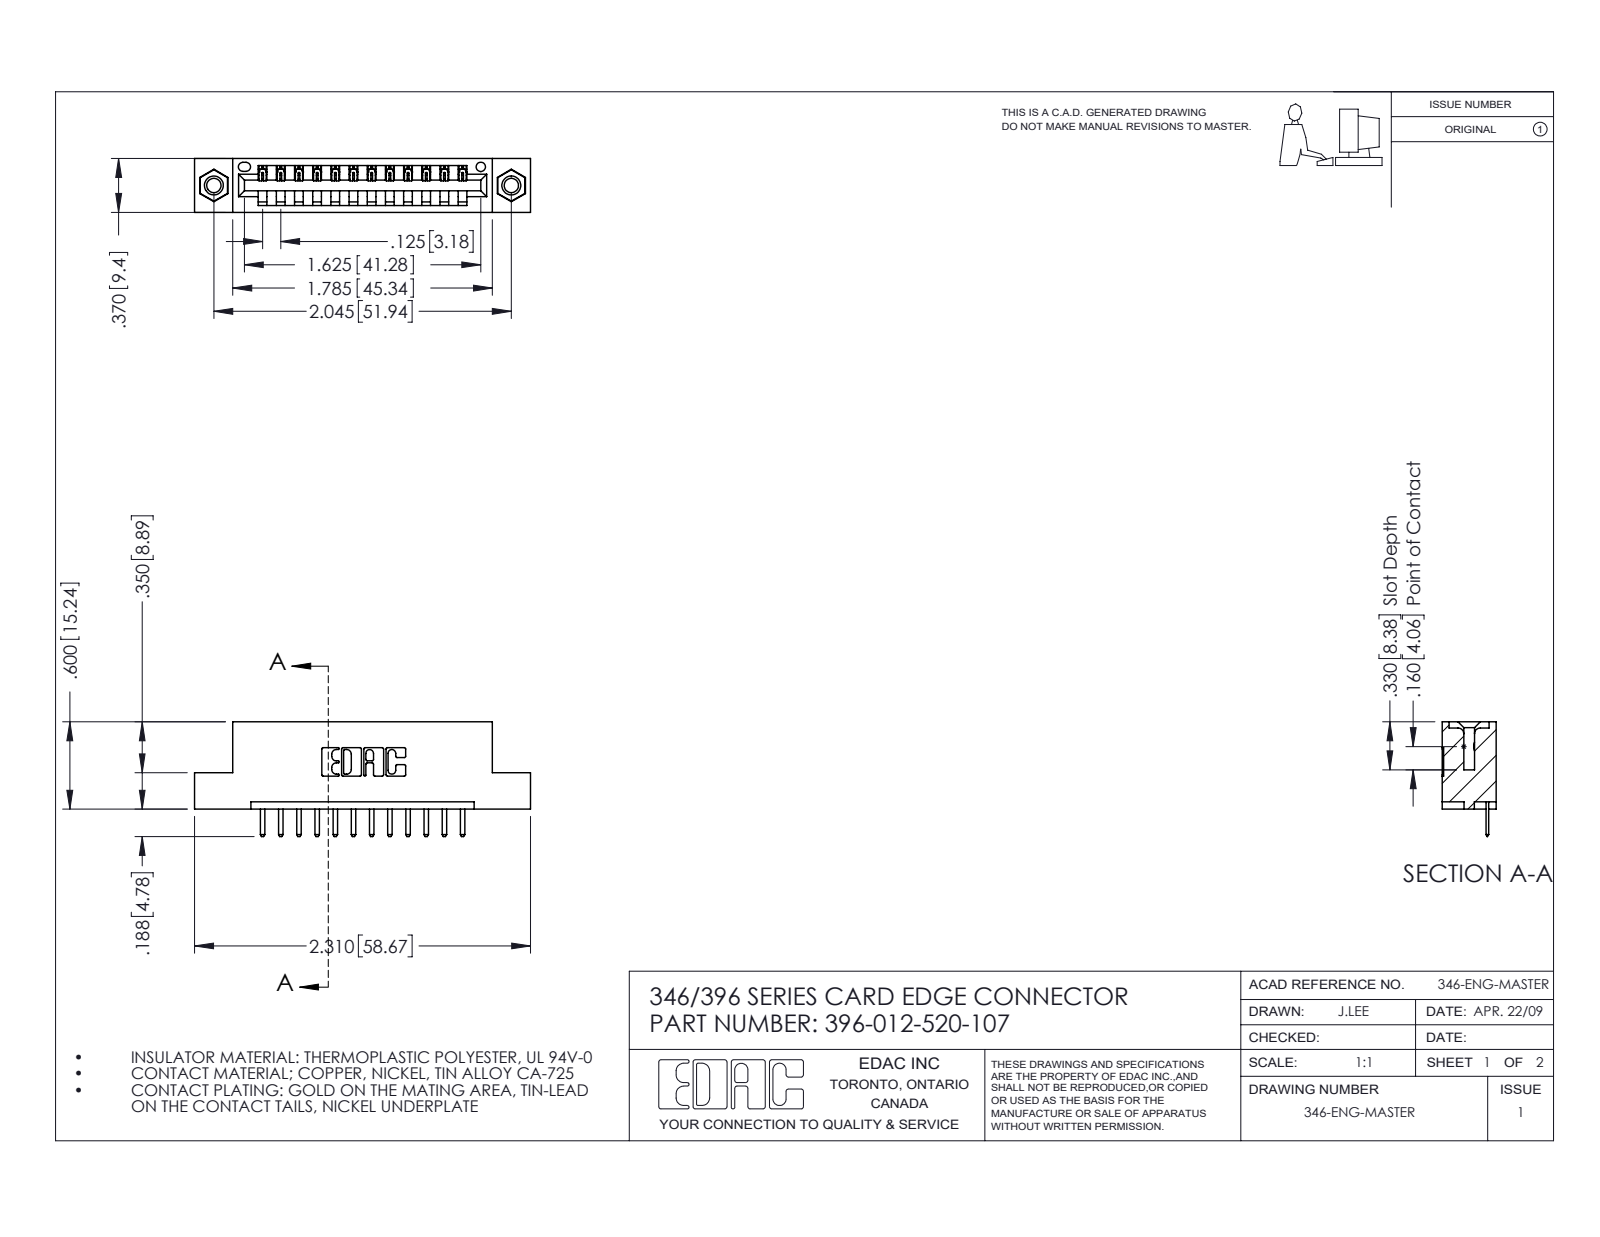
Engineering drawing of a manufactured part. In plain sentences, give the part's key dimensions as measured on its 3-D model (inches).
The part is named "346 Part_Flush Mounting Lugs - 0.156 Dia-TI; 345-250-001_345-250-005-103; 345-292-001_345-293-120; 396-012-520-107". Its 3-D file was written by "SolidWorks 2016 (CONFIG_CONTROL_DESIGN)". It is 15 solids with 926 faces: 612 planar, 298 cylindrical and 16 other. Overall it measures 2.31 by 0.788 by 0.37 inches. Its volume is 0.327 cubic inches and its surface area 9.76 square inches. Round holes: 2 of diameter 0.098, 2 of diameter 0.125, 2 of diameter 0.156, 1 of diameter 0.064. Round bosses or shafts: 2 of diameter 0.155. Partial cylindrical surfaces (rounded edges, fillets, slot ends): 26 of radius 0.01, 24 of radius 0.006, 22 of radius 0.01, 6 of radius 0.007, 6 of radius 0.031, 3 of radius 0.026, 2 of radius 0.031, 2 of radius 0.04. The main face-to-face distances are 0.25, 0.37, 0.048, 0.322, 0.148, 0.222, 0.1, 0.174, 0.072, 0.298. The hole center spacings are 0.246, 1.839, 2.045.
